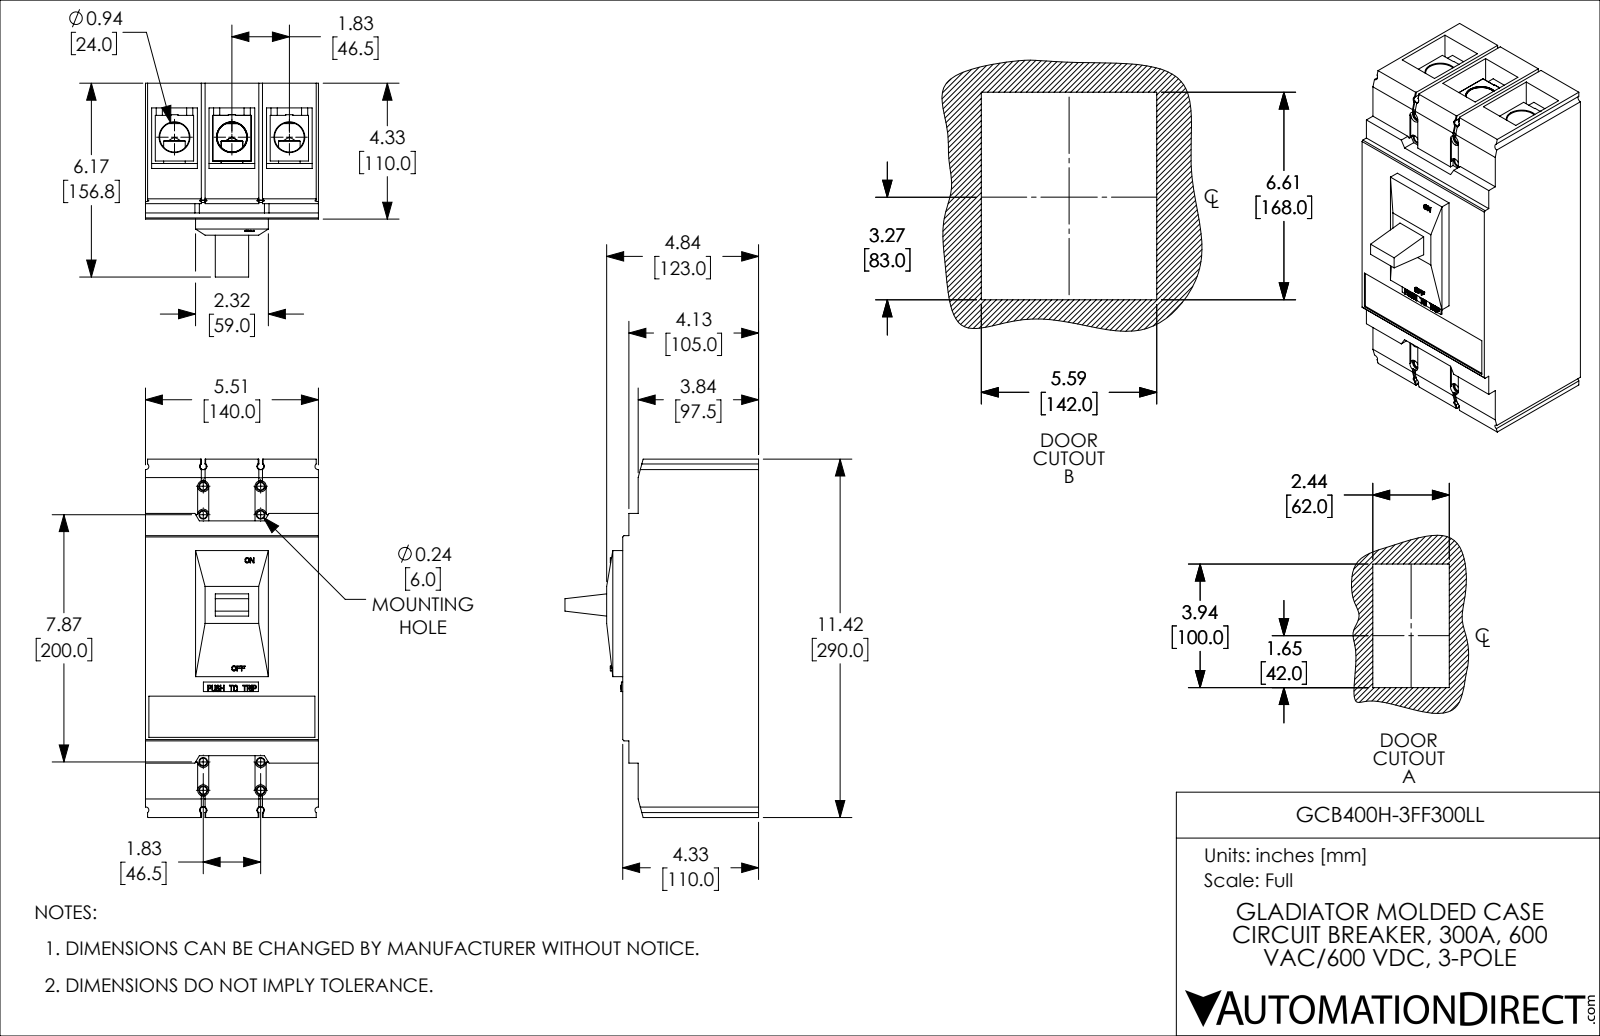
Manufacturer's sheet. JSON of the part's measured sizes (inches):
{"part_name": "GCB400H-3FF300LL", "step_written_by": "SolidWorks 2021 (CONFIG_CONTROL_DESIGN)", "units": "inches", "bodies": {"solids": 26, "faces": 1319, "planar": 935, "cylindrical": 200, "other": 184}, "overall_size": [11.417, 6.173, 5.512], "volume_in3": 245.8, "surface_area_in2": 525.8, "round_holes": [[0.236, 8], [0.413, 6], [0.594, 6], [0.688, 6], [0.197, 4], [0.354, 4], [0.945, 3]], "round_bosses_or_shafts": [[0.575, 6], [0.394, 6], [0.75, 1]], "partial_cylinders_radius": [[0.098, 28], [0.039, 8], [0.177, 4]], "face_to_face_distances": [1.831, 5.512, 0.492, 1.457, 0.118, 1.339, 1.772, 1.713, 1.949, 0.197], "hole_center_spacings": [1.831, 0.968, 1.089, 1.316, 8.514, 9.415, 10.042, 0.63]}
